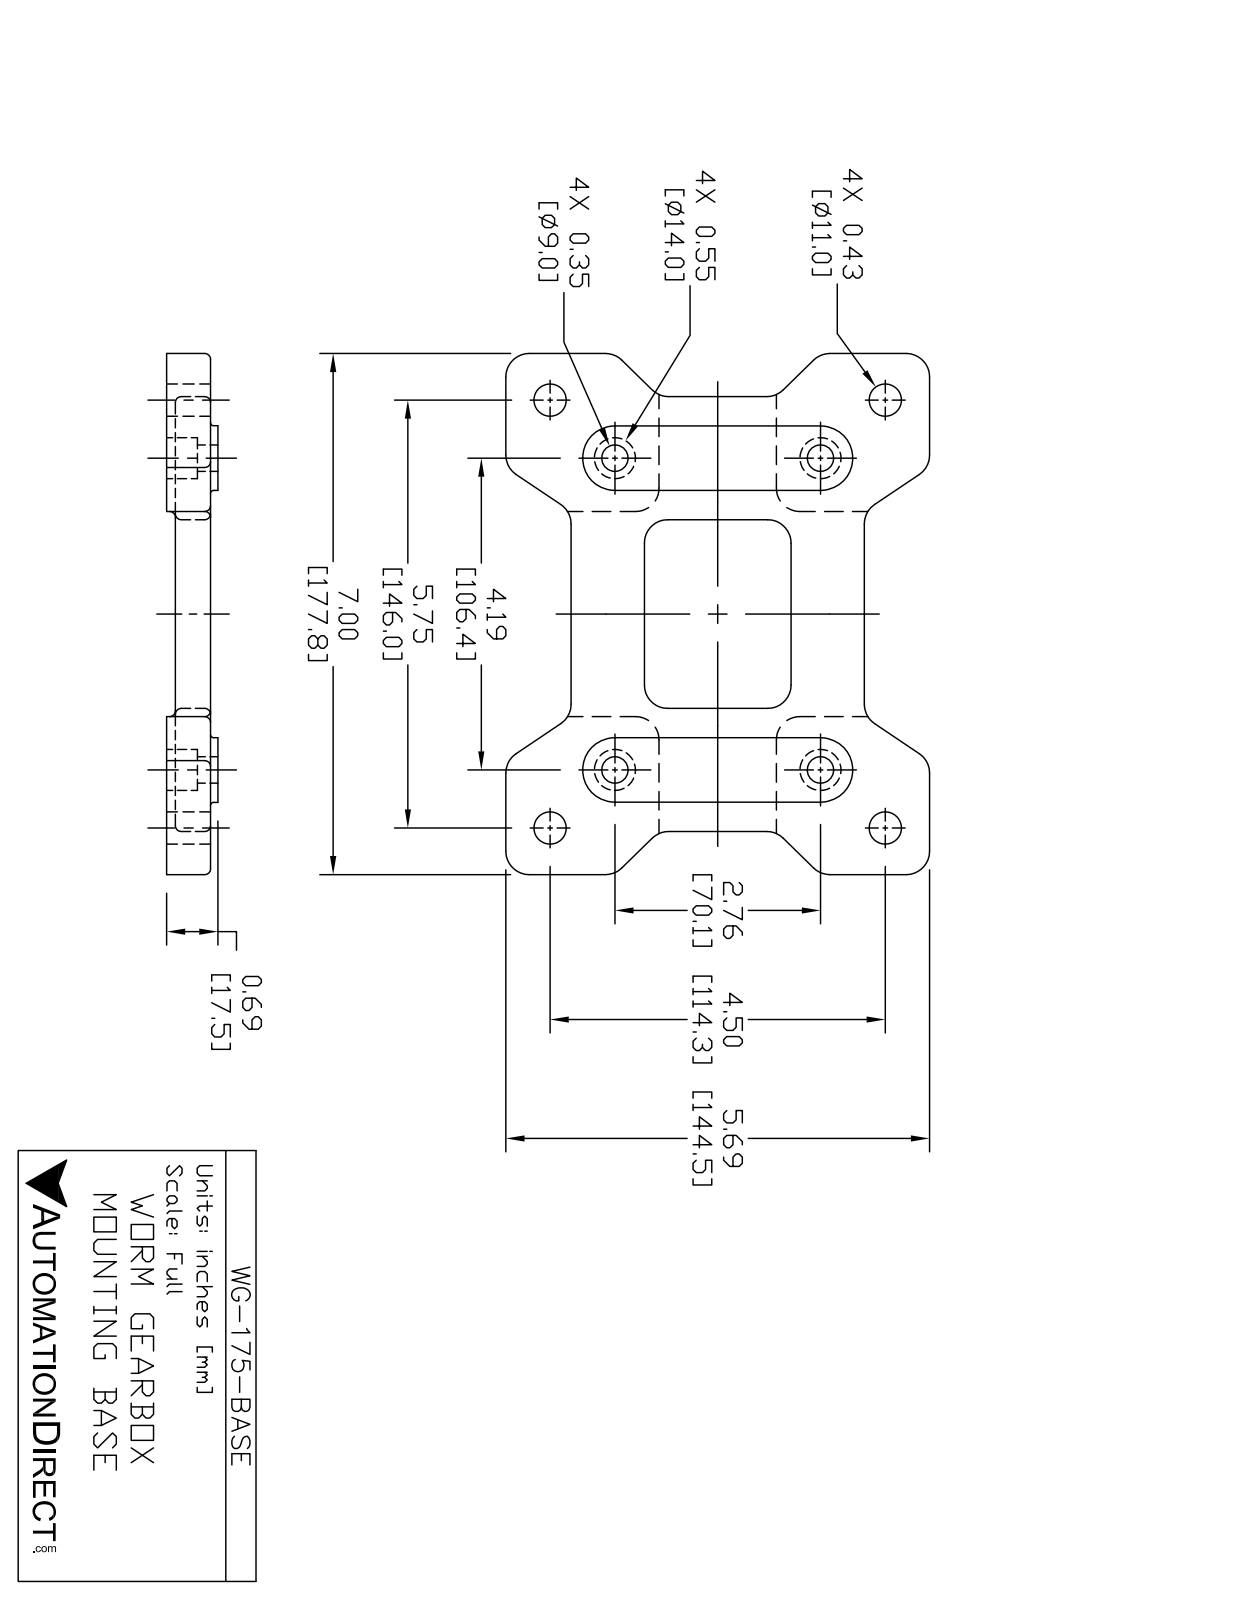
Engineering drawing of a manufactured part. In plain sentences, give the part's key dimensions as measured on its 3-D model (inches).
The part is named "WG-175-BASE". Its 3-D file was written by "SolidWorks 2015 (CONFIG_CONTROL_DESIGN)". It is 1 solid with 128 faces: 48 planar, 70 cylindrical and 10 other. Overall it measures 7 by 5.689 by 0.689 inches. Its volume is 14.09 cubic inches and its surface area 79.61 square inches. Round holes: 4 of diameter 0.354, 4 of diameter 0.433, 4 of diameter 0.551. Partial cylindrical surfaces (rounded edges, fillets, slot ends): 28 of radius 0.315, 4 of radius 0.039, 4 of radius 0.079, 4 of radius 0.433. The main face-to-face distances are 0.591, 0.118, 0.472, 0.689, 0.571, 0.098, 0.878, 4.811, 1.86, 3.829. The hole center spacings are 1.168, 3.713, 5.044, 6.153, 2.76, 4.189, 4.5, 5.017.
